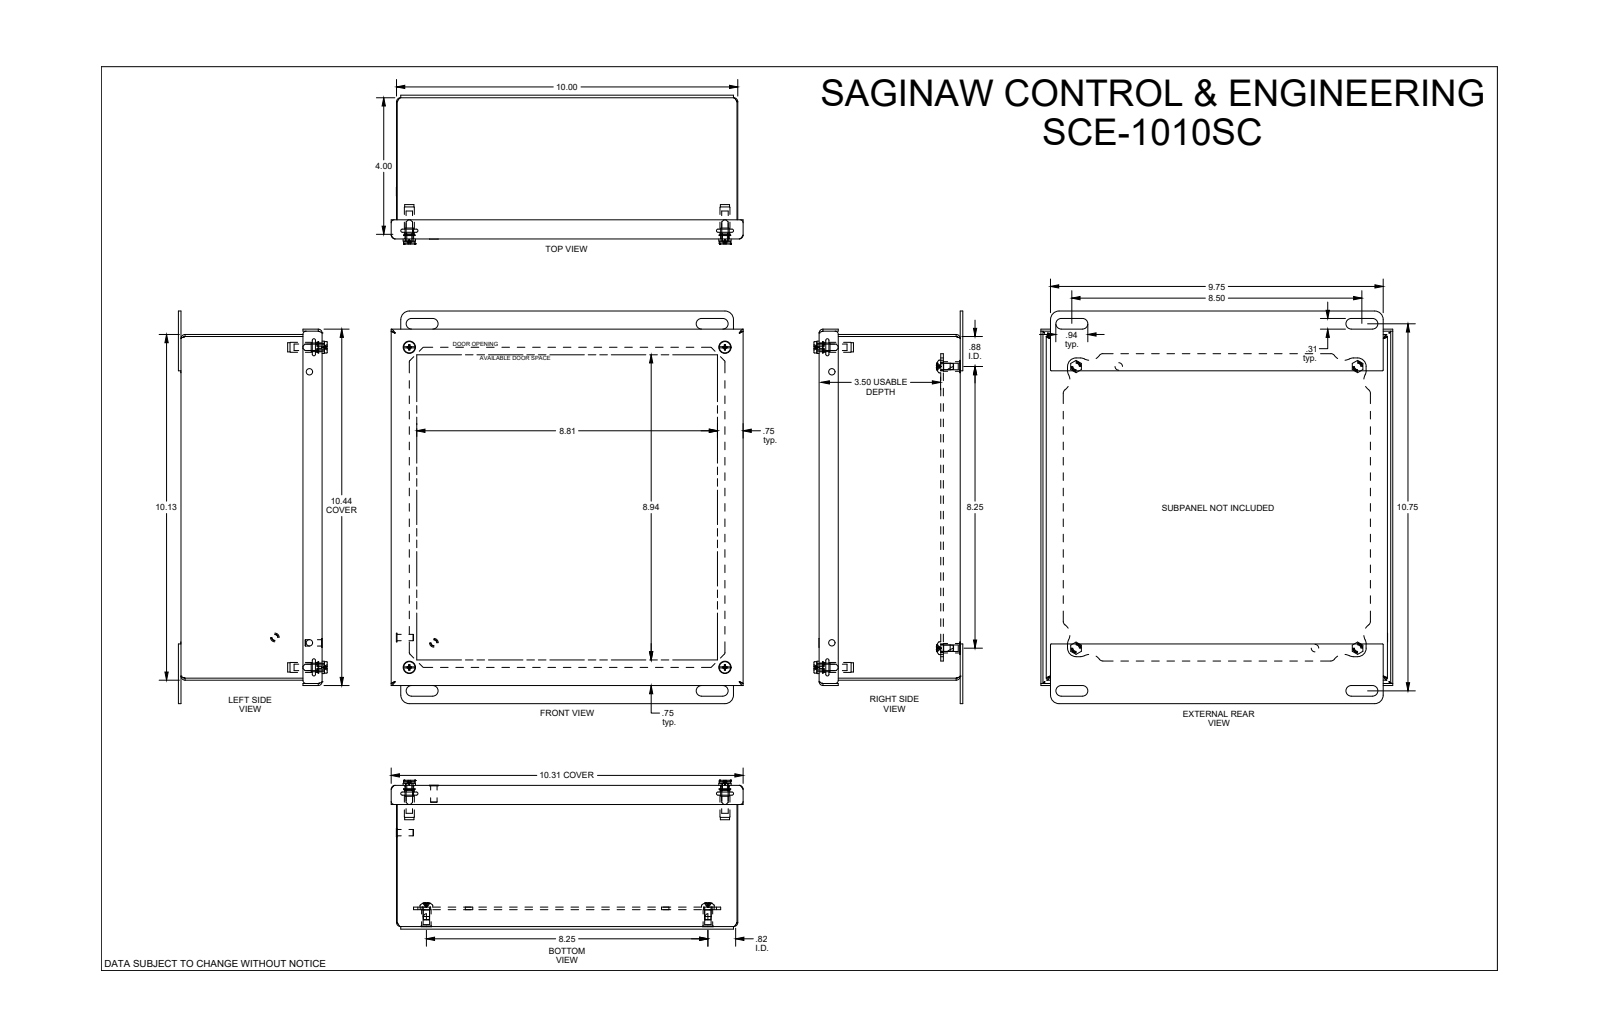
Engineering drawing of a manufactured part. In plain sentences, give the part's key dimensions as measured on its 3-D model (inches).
The part is named "SCE-1010SC". Its 3-D file was written by "SolidWorks 2019 (AUTOMOTIVE_DESIGN)". It is 28 solids with 805 faces: 328 planar, 207 cylindrical and 270 other. Overall it measures 11.5 by 10.313 by 4.361 inches. Its volume is 33.67 cubic inches and its surface area 1 075 square inches. Round holes: 8 of diameter 0.19, 8 of diameter 0.25, 4 of diameter 0.22, 4 of diameter 0.266, 4 of diameter 0.281, 4 of diameter 0.317, 2 of diameter 0.187, 2 of diameter 0.218, 1 of diameter 0.193. Round bosses or shafts: 10 of diameter 0.188, 4 of diameter 0.437, 4 of diameter 0.373, 4 of diameter 0.362, 4 of diameter 0.34, 4 of diameter 0.334, 4 of diameter 0.292, 4 of diameter 0.28. Partial cylindrical surfaces (rounded edges, fillets, slot ends): 16 of radius 0.125, 16 of radius 0.25, 12 of radius 0.06, 8 of radius 0.005, 8 of radius 0.05, 8 of radius 0.063, 8 of radius 0.156, 8 of radius 0.255. The main face-to-face distances are 0.06, 4.075, 4.135, 4.015, 3.505, 0.075, 0.57, 0.51, 3.565, 0.495. The hole center spacings are 8.827, 0.753, 8.25, 8.768, 12.419, 8.768, 9.25, 9.375.
